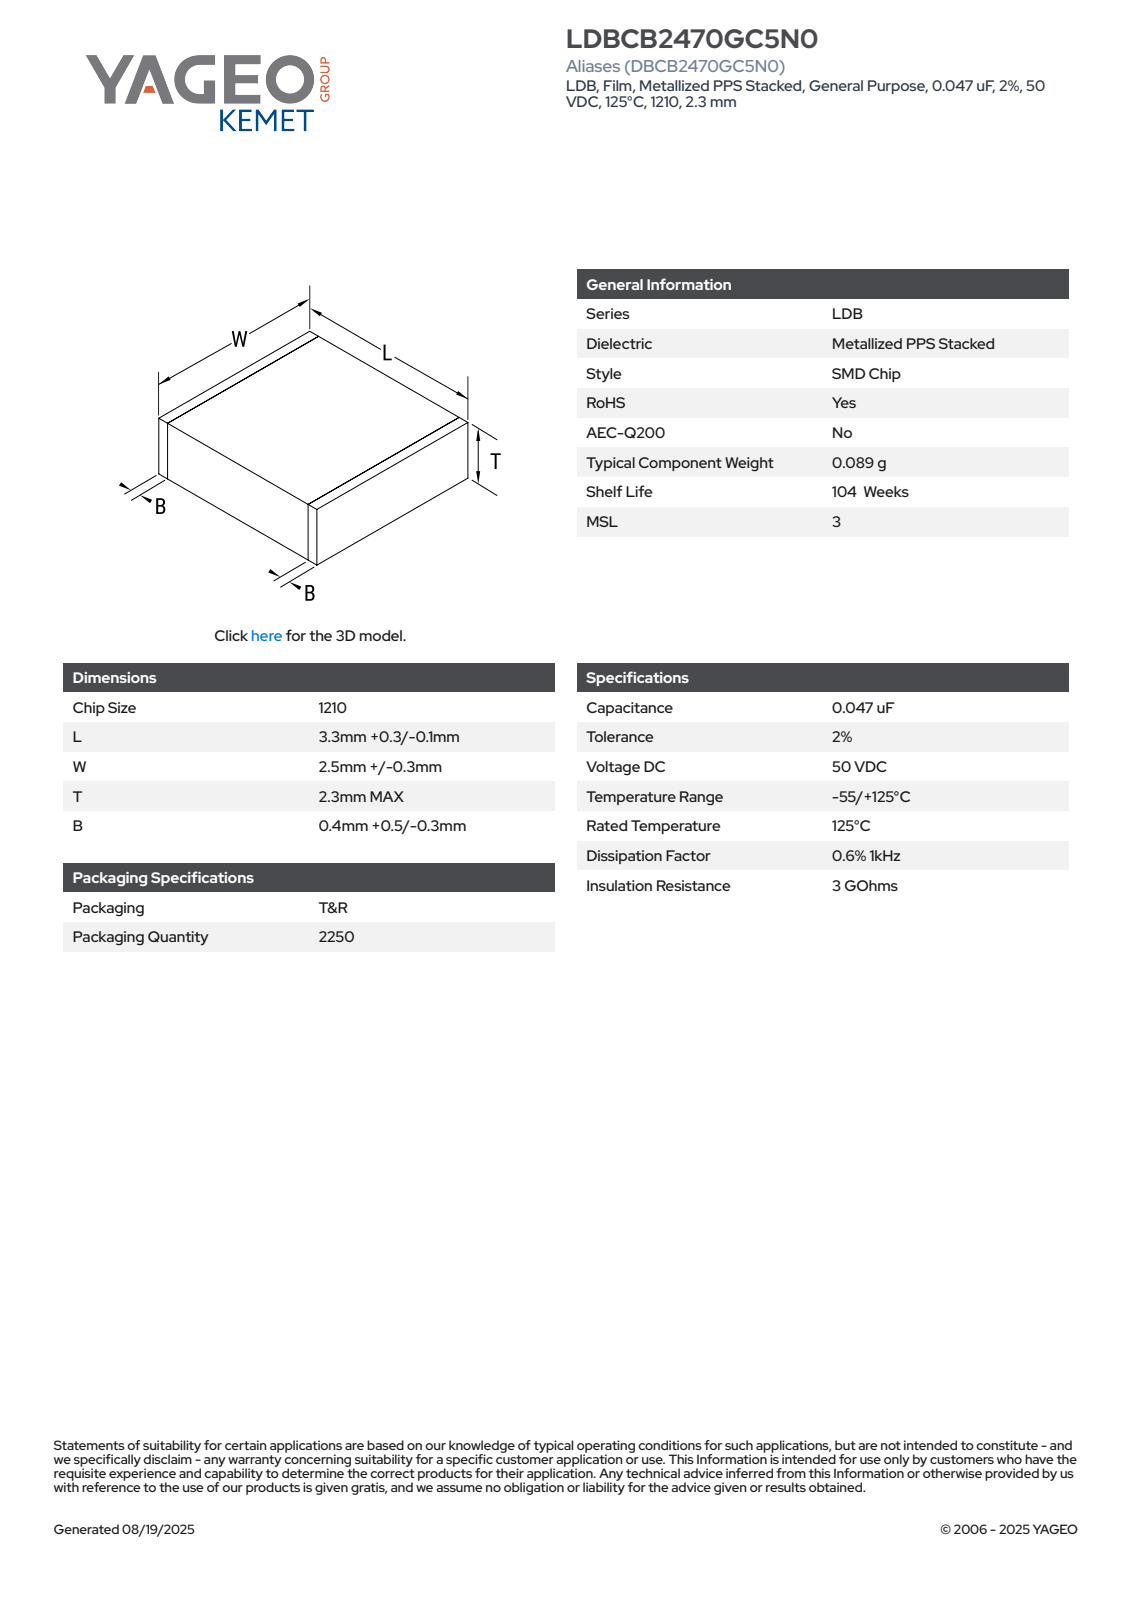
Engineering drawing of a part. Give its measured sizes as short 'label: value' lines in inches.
name: CFS_LDELDB_1210_L3.6W2.8T2.3B0.9
written by: SolidWorks 2020 (AUTOMOTIVE_DESIGN)
unit: in
bodies: 4 solids, 73 faces (73 planar, 0 cylindrical, 0 other)
size: 0.142 × 0.11 × 0.091
volume: 0.001 in³; area: 0.078 in²
face distances: 0.09, 0.142, 0.109, 0.09, 0.11, 0.091, 0.11, 0.02, 0.122, 0.102
